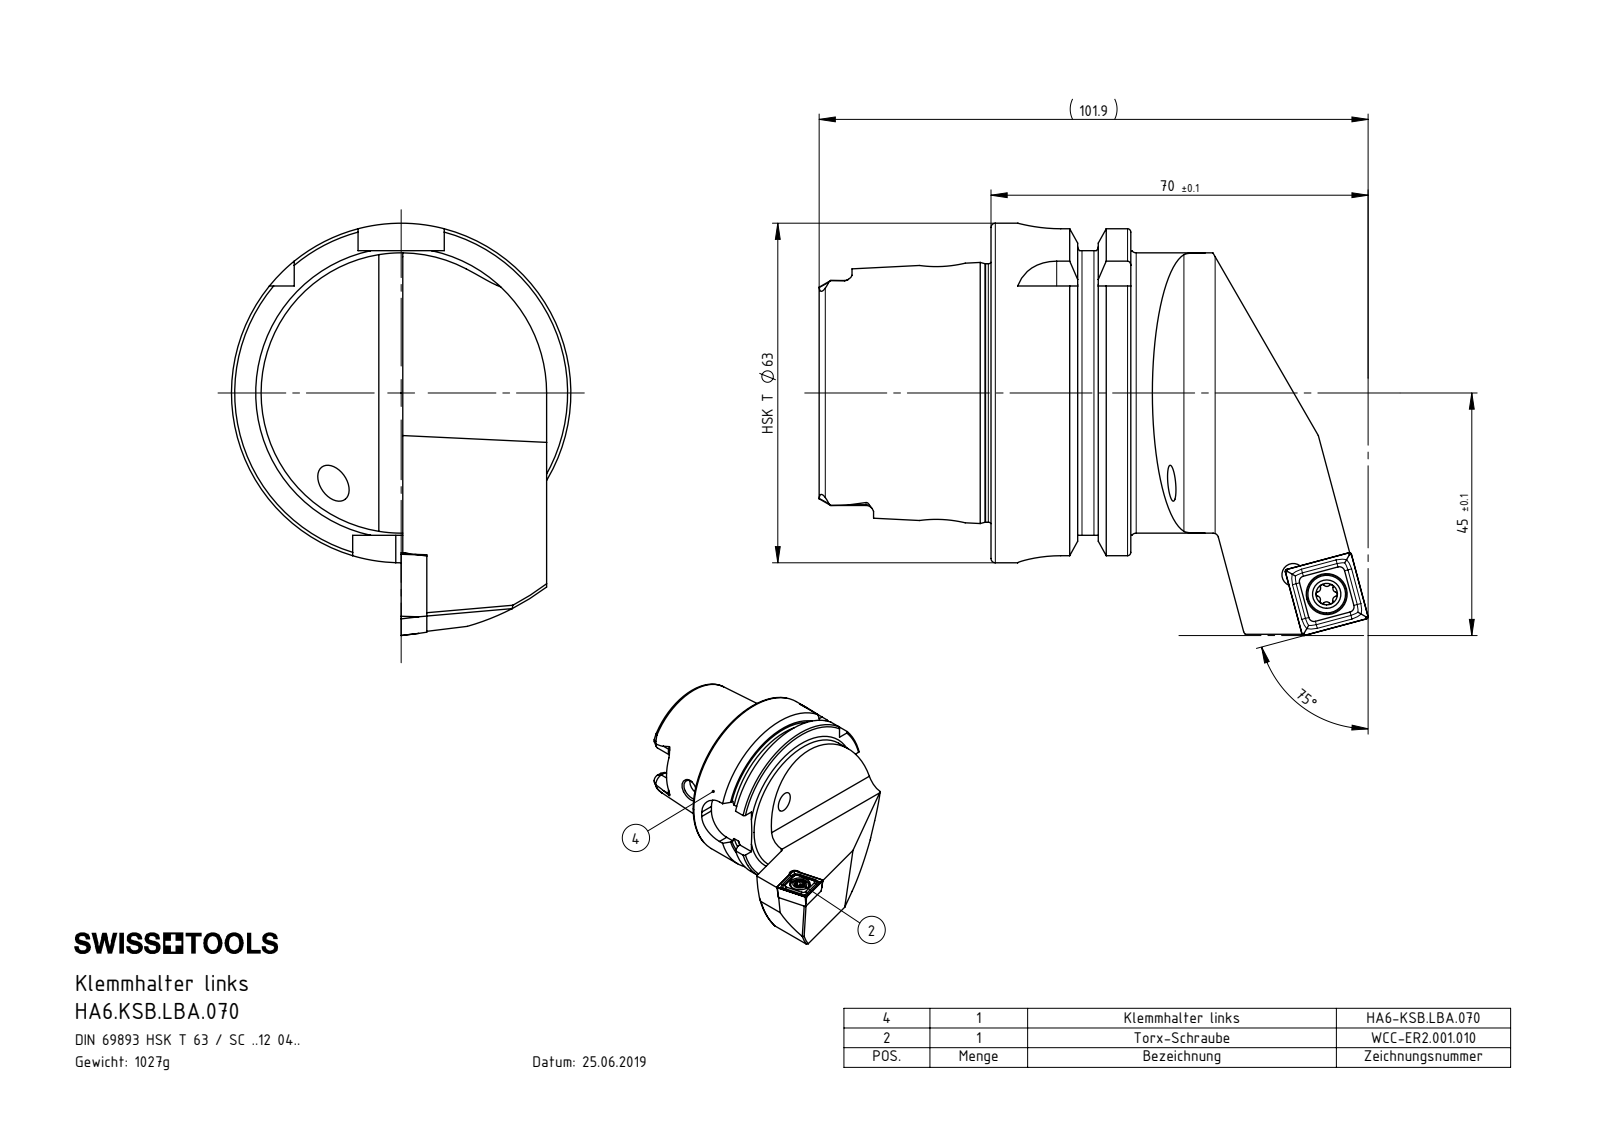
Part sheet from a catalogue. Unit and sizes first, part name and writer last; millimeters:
Units: millimetres
Overall size (bounding box): 101.9 × 76.5 × 63
Round holes (diameter × count): ⌀5 ×3, ⌀4.2 ×2, ⌀5.5 ×1, ⌀6 ×1, ⌀7.5 ×1, ⌀7.6 ×1, ⌀8.4 ×1, ⌀10 ×1, ⌀17 ×1, ⌀19 ×1, ⌀34 ×1, ⌀40 ×1
Round bosses / shafts (diameter × count): ⌀63 ×1, ⌀54.95 ×1, ⌀52 ×1, ⌀47.94 ×1, ⌀7 ×1, ⌀6 ×1, ⌀5 ×1
Partial cylindrical surfaces — rounded edges, fillets, slot ends (radius × count): R0.39 ×6, R1.4 ×6, R2.88 ×4, R8 ×4, R0.69 ×3, R0.69 ×3, R6 ×1, R27 ×1
Main face-to-face distances: 25.95, 26.7, 16, 9.95, 31.9, 41.85, 57.85, 22.24, 4.46, 52.8
Hole centre spacings: 7.07, 7.17, 59.57, 66.61, 66.72
Volume: 130 769 mm³ · Surface area: 30 627 mm²
Bodies: 6 solids, 327 faces (86 planar, 90 cylindrical, 151 other)
Part name (STEP PRODUCT): KVT_MB_600_060; SCMT120404; HA6.KSB.LBA.070; HA6-KSB.LBA.070_A_Fertigbearbeitung (+1 more)
STEP written by: SolidWorks 2017 (AUTOMOTIVE_DESIGN)
